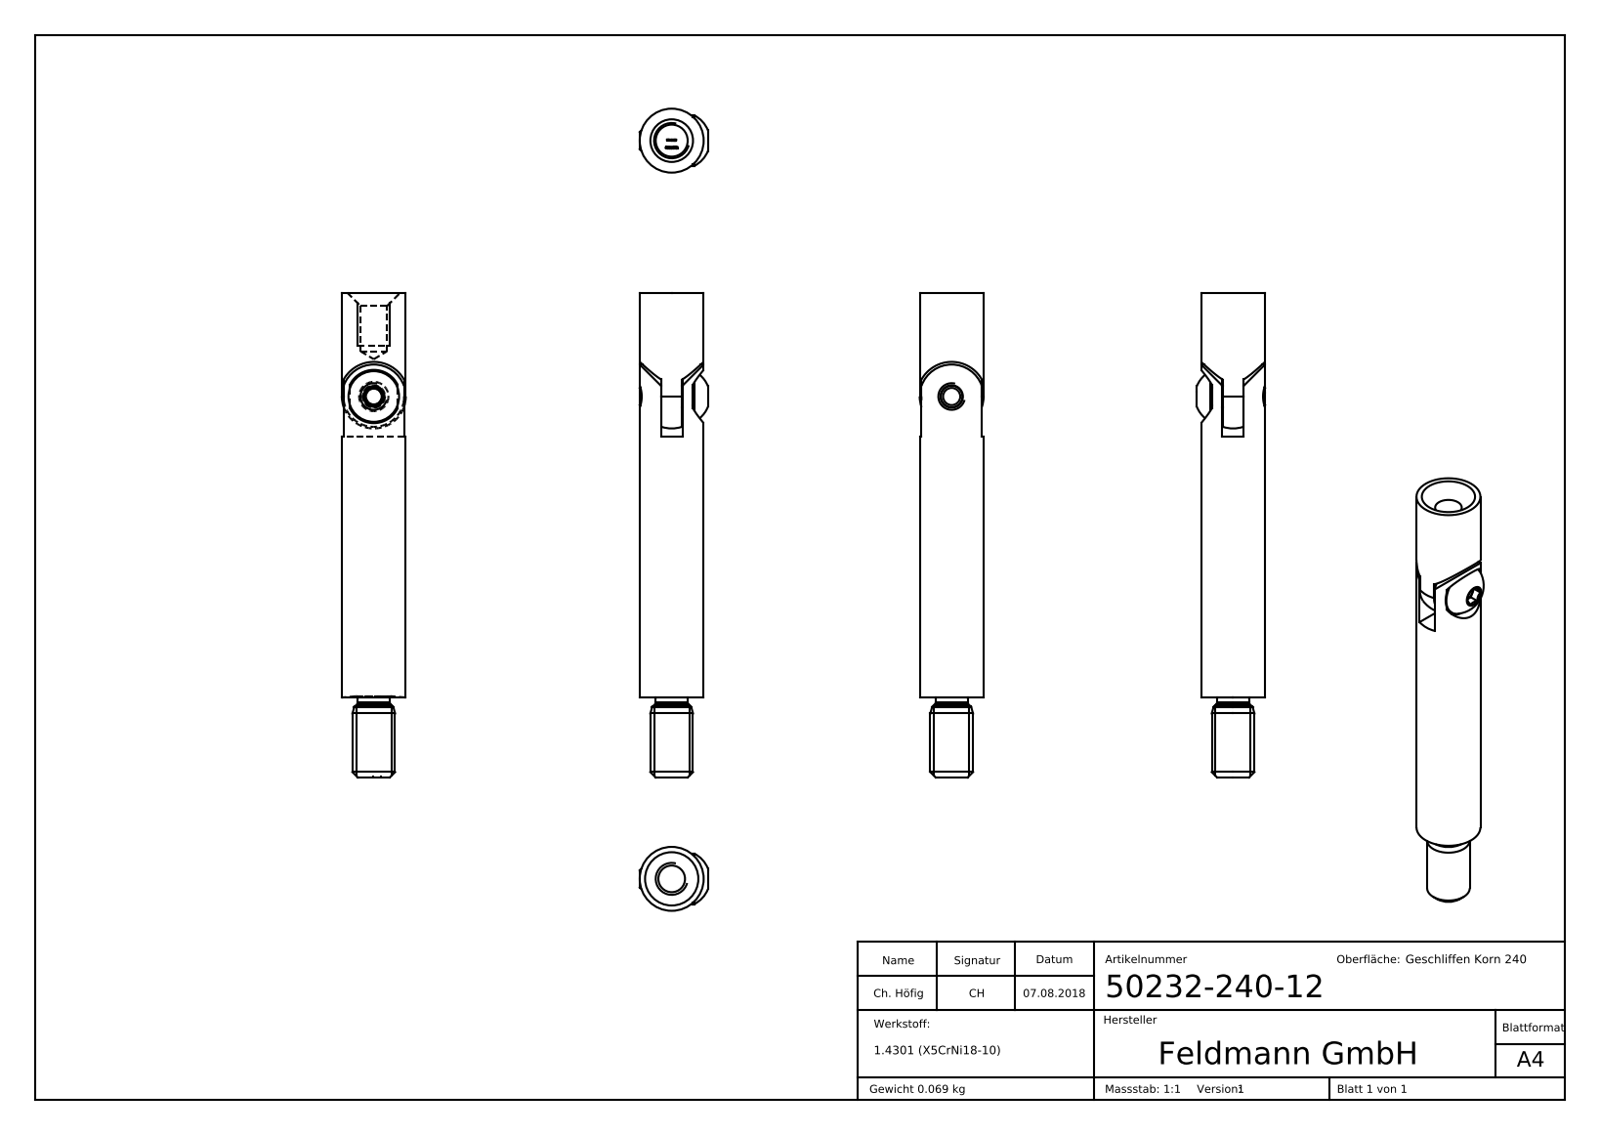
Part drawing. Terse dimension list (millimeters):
name: 50232-240-12; 50232-240-12 Teil3_M5x10; 50232-240-12 Teil1_50232-240-12 Teil1; 50232-240-12 Teil2_50232-240-12 Teil2
written by: SolidWorks 2015 (CONFIG_CONTROL_DESIGN)
unit: mm
bodies: 3 solids, 330 faces (158 planar, 26 cylindrical, 146 other)
size: 91 × 12.8 × 12
volume: 8 734 mm³; area: 4 697 mm²
holes: 1× ⌀4.2, 1× ⌀5, 1× ⌀5.5
bosses: 1× ⌀12, 1× ⌀9.5, 1× ⌀8, 1× ⌀6, 1× ⌀4.02
rounds: 1× R5, 1× R6, 1× R6.5
face distances: 4, 6, 2, 2.12, 3.88, 3.75, 3.87, 5.87, 27, 64
